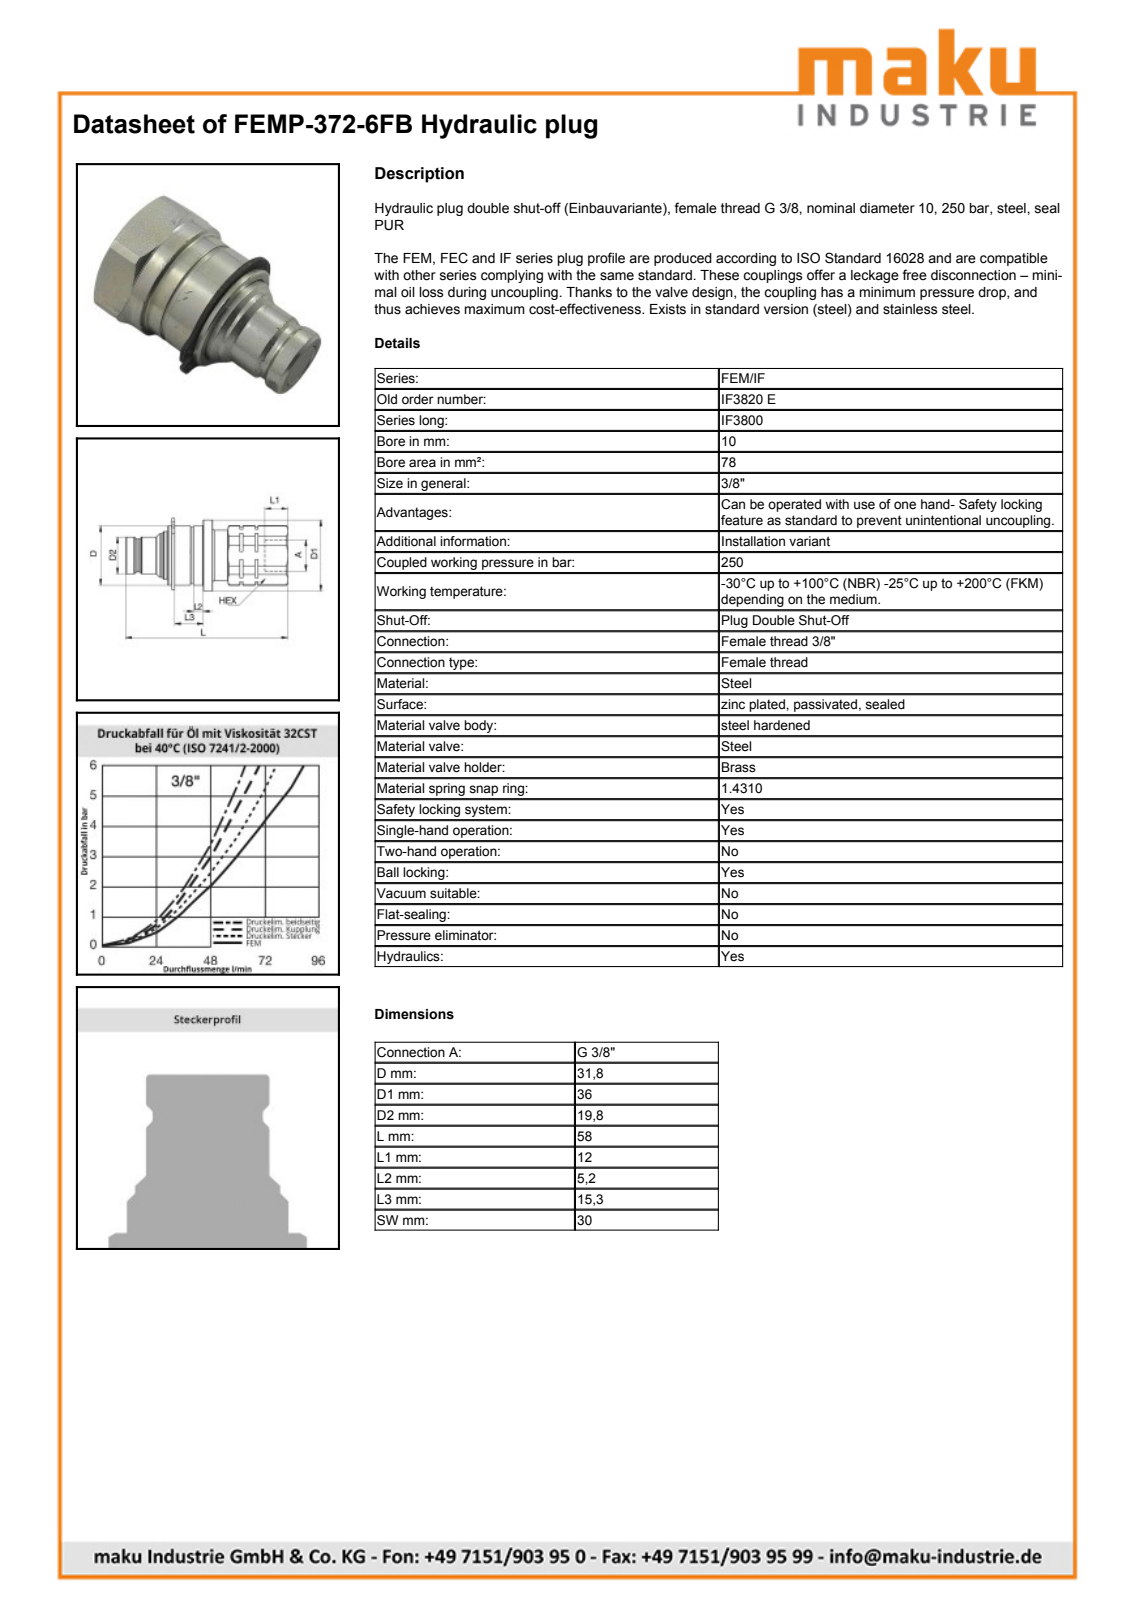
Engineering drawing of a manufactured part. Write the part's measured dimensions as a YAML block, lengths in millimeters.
part_name: "FEMP-372-6FB"
step_written_by: "SolidWorks 2009 (AUTOMOTIVE_DESIGN)"
units: millimeters
bodies: {solids: 1, faces: 125, planar: 23, cylindrical: 48, other: 54}
overall_size: [58, 40, 36]
volume: 37593
surface_area: 9227
round_holes:
  - {diameter: 2.5, count: 2}
  - {diameter: 12.65, count: 1}
  - {diameter: 14.5, count: 1}
  - {diameter: 15, count: 1}
  - {diameter: 26.2, count: 1}
round_bosses_or_shafts:
  - {diameter: 35.8, count: 1}
  - {diameter: 31.8, count: 1}
  - {diameter: 30.2, count: 1}
  - {diameter: 26, count: 1}
  - {diameter: 23.3, count: 1}
  - {diameter: 19.75, count: 1}
  - {diameter: 17.6, count: 1}
partial_cylinders:
  - {radius: 3, count: 2}
  - {radius: 8, count: 2}
  - {radius: 17.8, count: 1}
  - {radius: 19.98, count: 1}
  - {radius: 20, count: 1}
face_to_face_distances: [36, 33.3, 1.5, 31.8, 24.7, 26.2, 58, 22.5, 2.2, 3.7]
hole_center_spacings: [17.18, 10]
